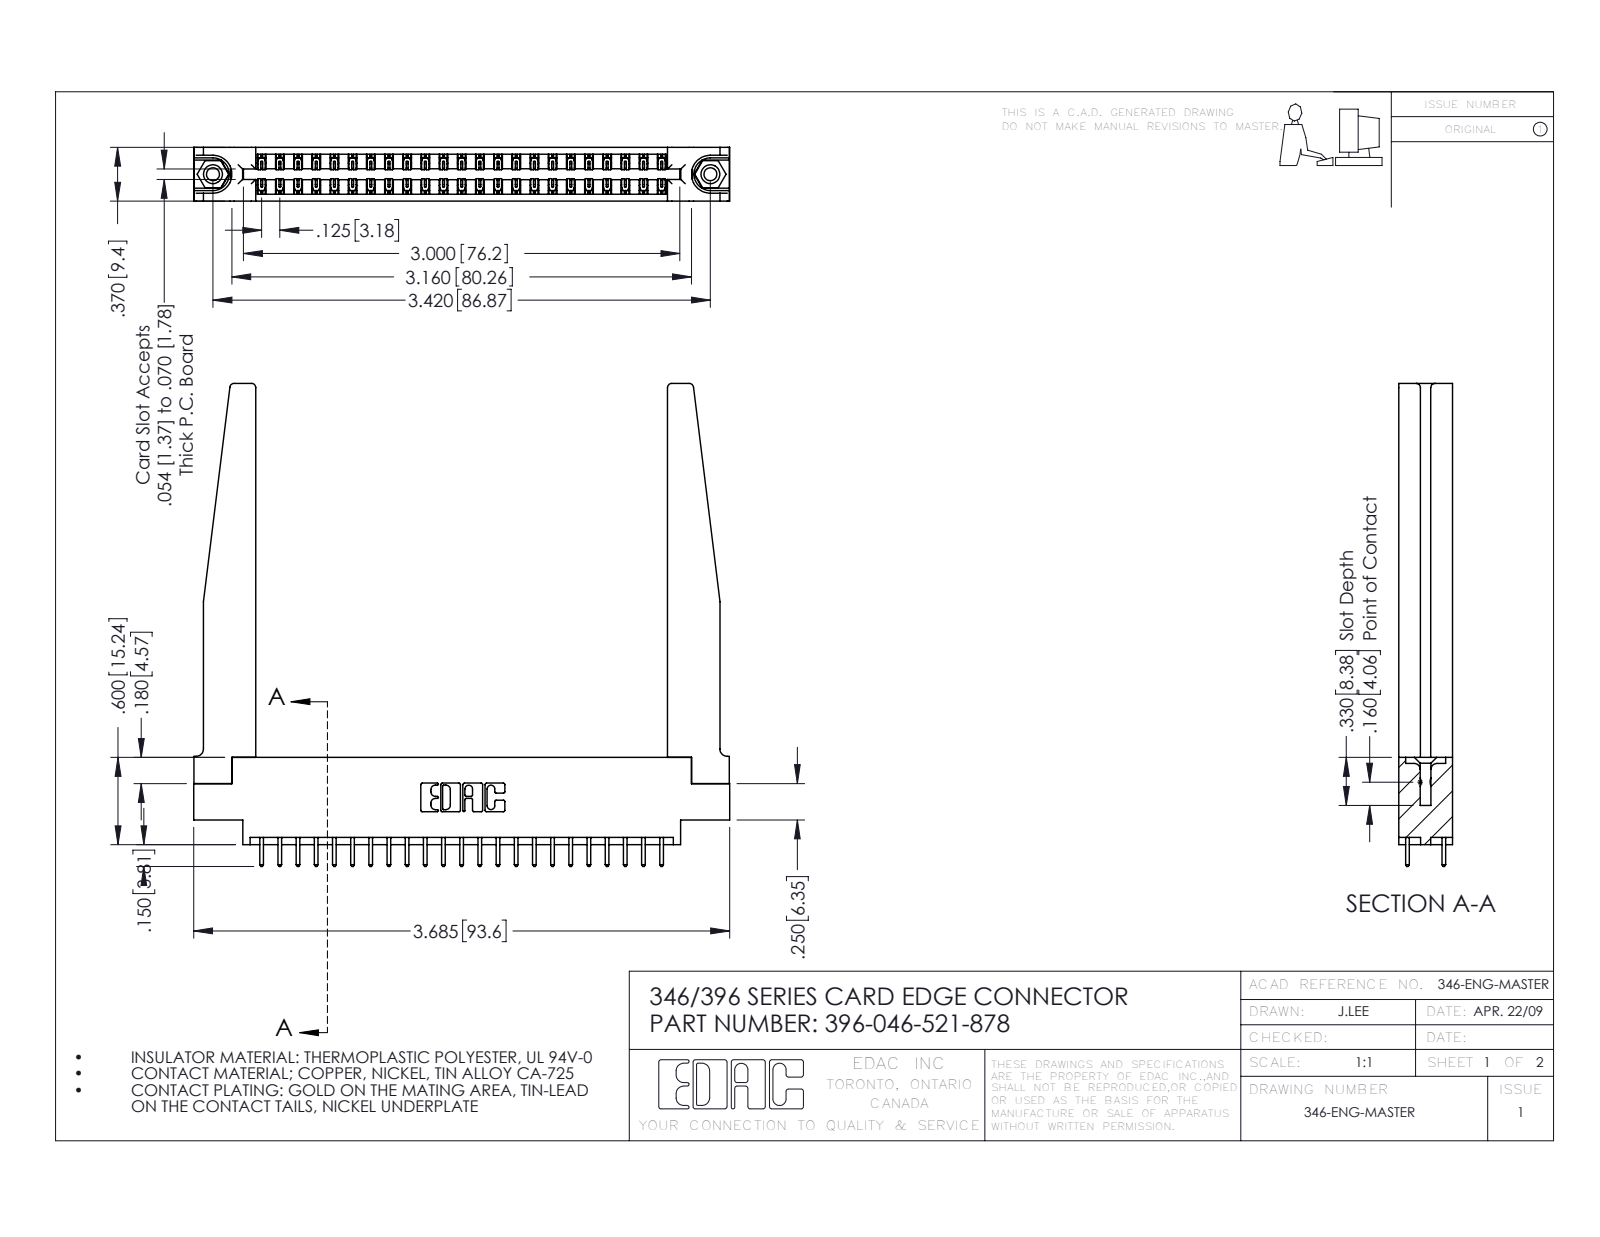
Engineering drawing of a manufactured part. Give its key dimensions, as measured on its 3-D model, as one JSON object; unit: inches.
{"part_name": "345-250-001_345-250-001-102; 345-292-001_345-293-121; 396-046-521-878; 346-220-078_345-220-078 (+1 more)", "step_written_by": "SolidWorks 2016 (CONFIG_CONTROL_DESIGN)", "units": "inches", "bodies": {"solids": 51, "faces": 2752, "planar": 1832, "cylindrical": 868, "other": 52}, "overall_size": [3.685, 3.32, 0.37], "volume_in3": 0.959, "surface_area_in2": 28.51, "round_holes": [[0.089, 2], [0.125, 2], [0.156, 2], [0.064, 1]], "round_bosses_or_shafts": [[0.155, 2]], "partial_cylinders_radius": [[0.006, 69], [0.01, 46], [0.01, 22], [0.03, 8], [0.007, 6], [0.031, 6], [0.026, 3], [0.014, 2]], "face_to_face_distances": [0.37, 0.048, 0.322, 0.072, 0.148, 0.15, 0.25, 0.298, 0.025, 0.275], "hole_center_spacings": [0.246, 3.212, 3.42]}
